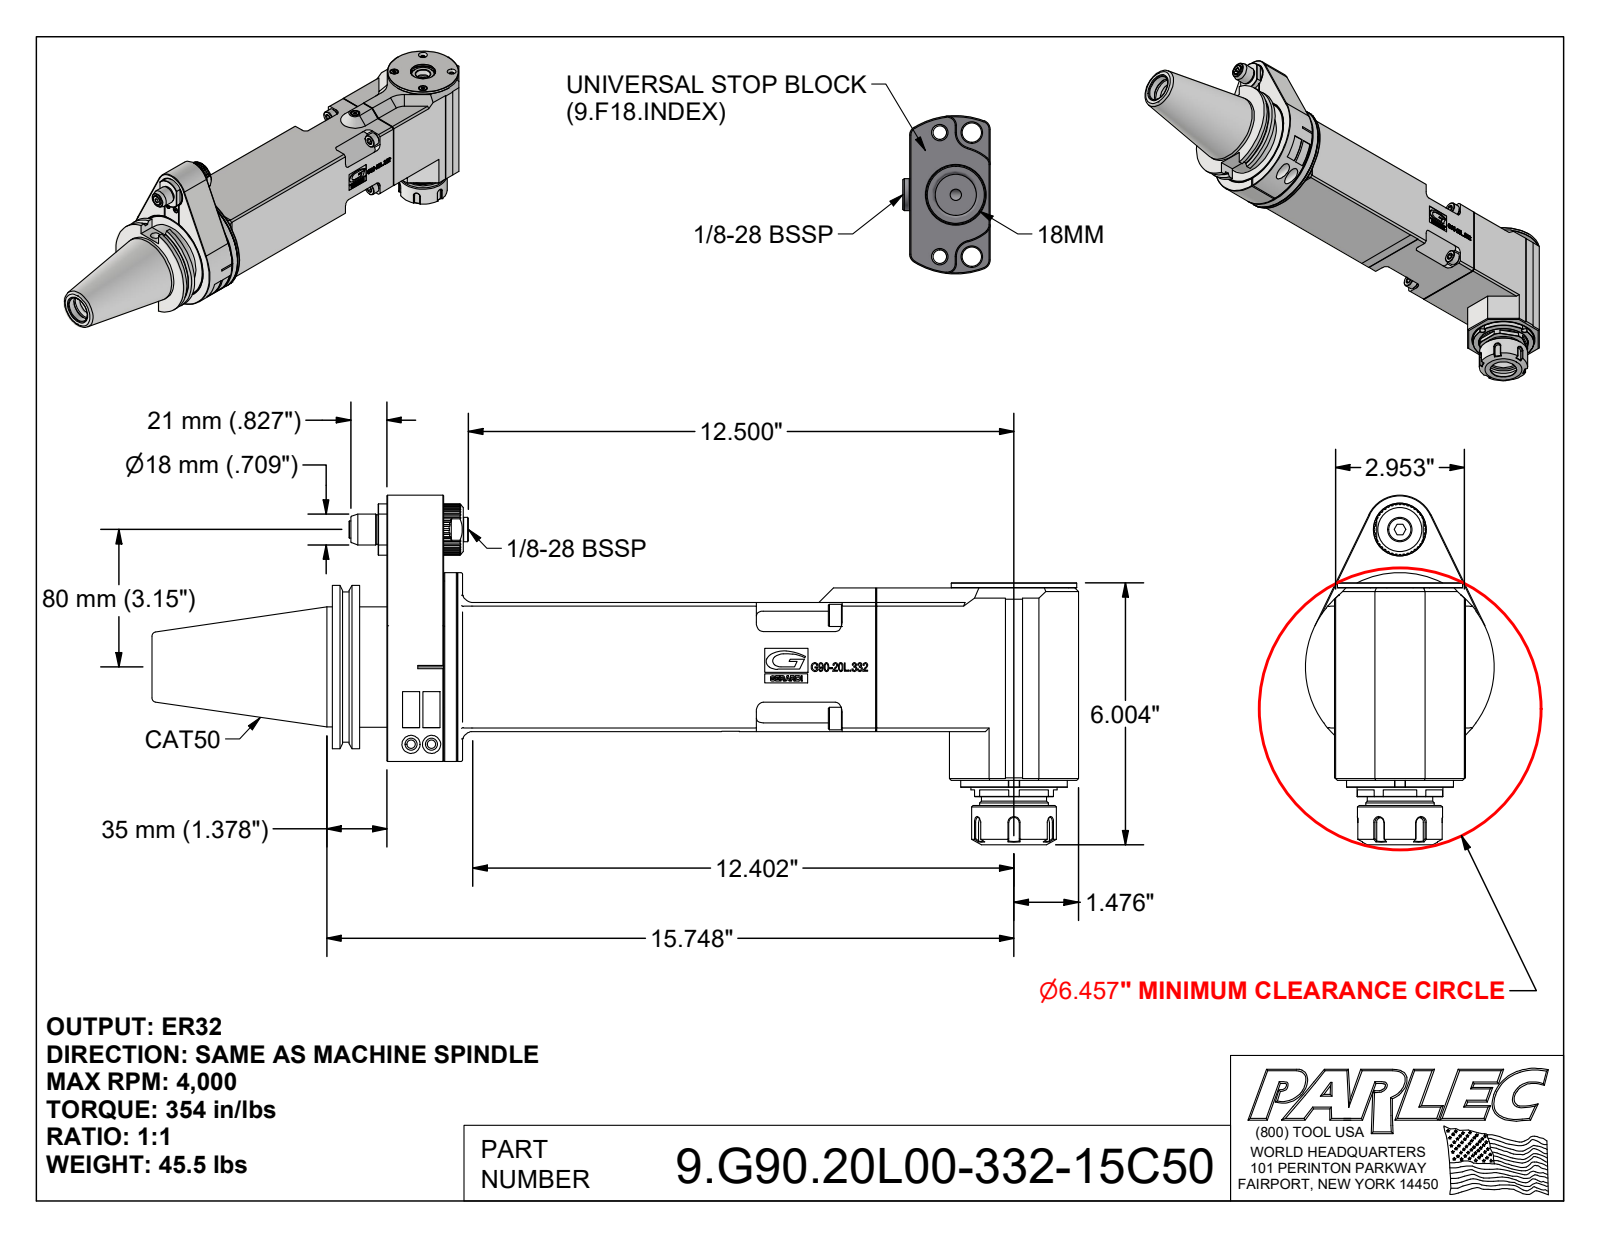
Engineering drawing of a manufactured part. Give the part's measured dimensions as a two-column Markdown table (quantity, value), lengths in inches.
| quantity | value |
| --- | --- |
| part name | 9.G90.20L00-332-15C50; 9_G90_20L00-332; 9_GA2_458_1 (Classic, Type 2, Cat50, 80mm) |
| STEP written by | Autodesk Inventor 2022 (AUTOMOTIVE_DESIGN) |
| units | inches |
| bodies | 20 solids, 1499 faces (731 planar, 264 cylindrical, 504 other) |
| overall size | 21.232 × 8.012 × 4.331 |
| volume | 173.5 in³ |
| surface area | 501.3 in² |
| round holes (diameter × count) | 0.197 × 14, 0.165 × 4, 0.335 × 4, 0.236 × 3, 0.157 × 2, 0.177 × 2, 0.276 × 2, 0.413 × 2, 0.591 × 2, 0.13 × 1, 0.354 × 1, 0.362 × 1 |
| round bosses / shafts (diameter × count) | 0.512 × 4, 0.394 × 2, 0.307 × 2, 4.331 × 1, 3.875 × 1, 3.593 × 1, 3.524 × 1, 2.874 × 1 |
| partial cylindrical surfaces (radius × count) | 0.118 × 10, 0.157 × 8, 0.098 × 6, 0.236 × 4, 0.085 × 2, 0.224 × 2, 0.079 × 1, 0.115 × 1 |
| main face-to-face distances | 2.953, 1.299, 0.315, 0.984, 0.626, 0.197, 0.118, 0.453, 0.02, 0.177 |
| hole center spacings | 1.87, 0.968, 2.645, 3.239, 3.613, 0.217, 0.538, 0.817 |
